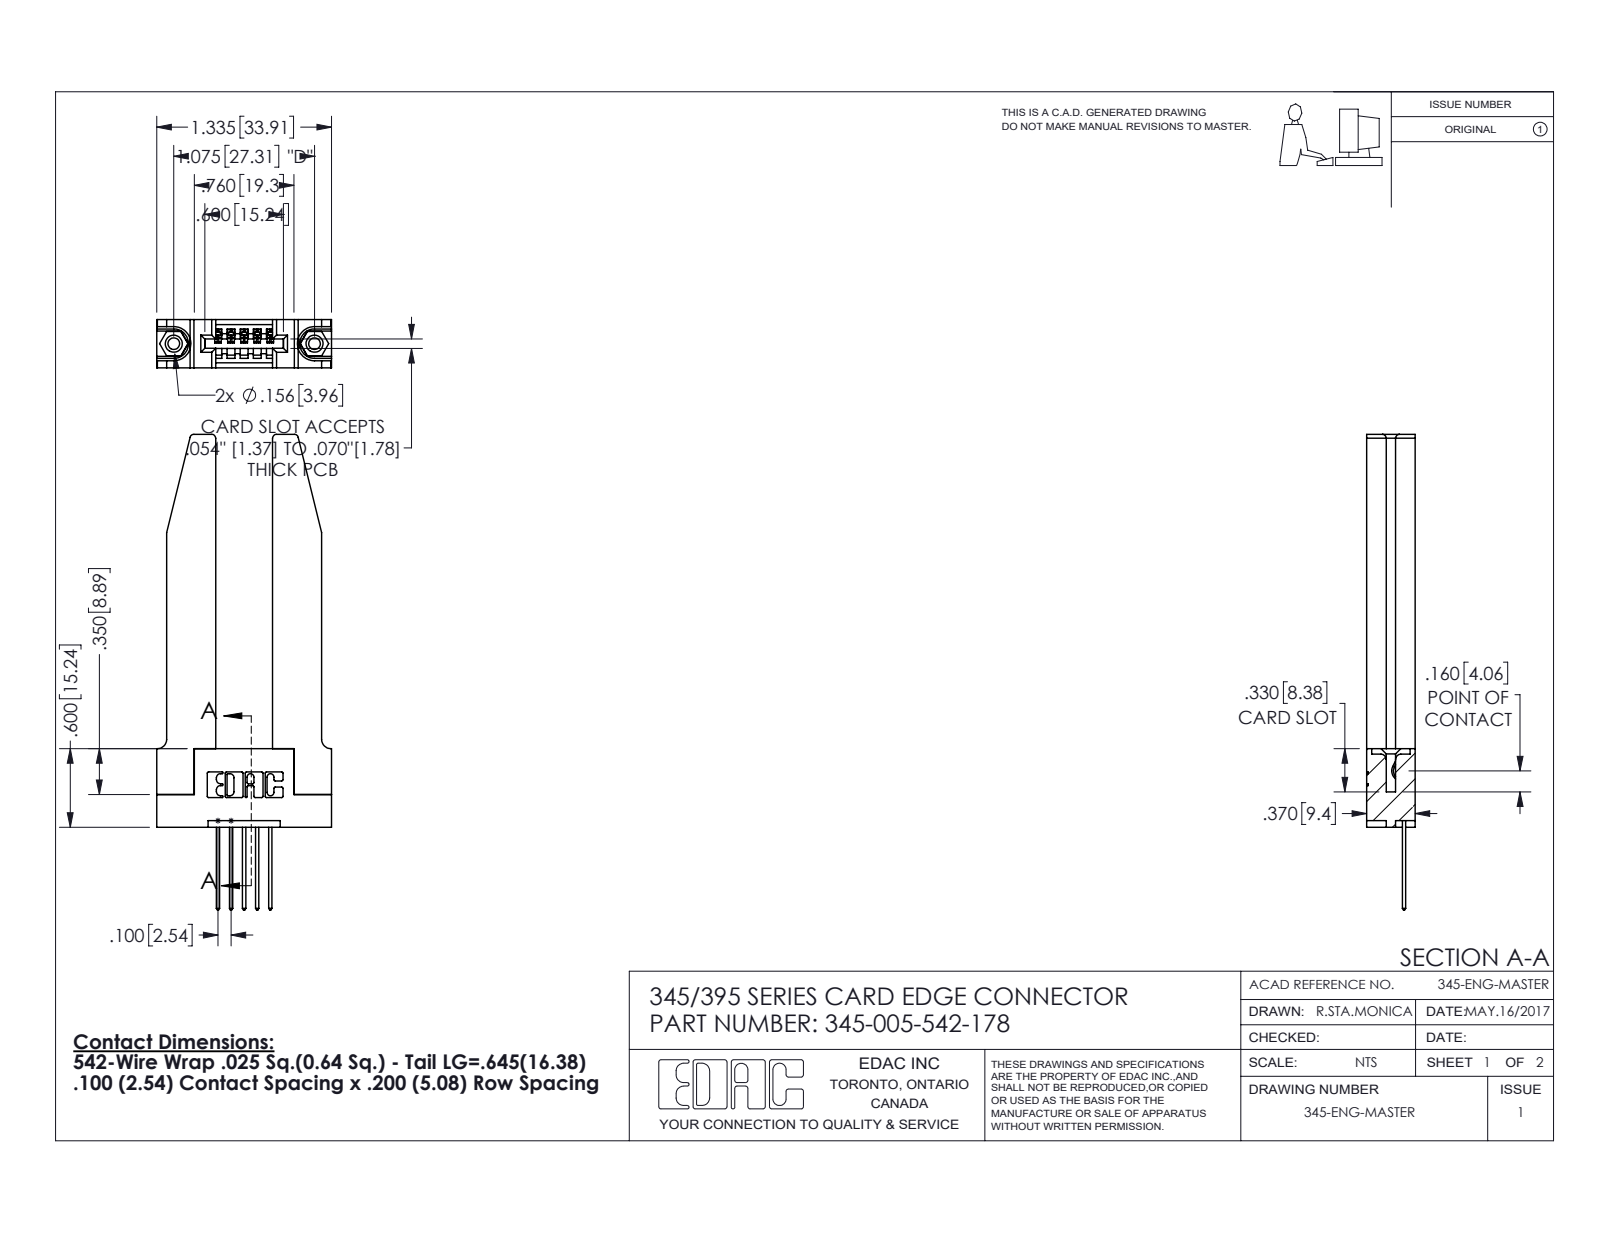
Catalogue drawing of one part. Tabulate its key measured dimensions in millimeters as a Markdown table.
| quantity | value |
| --- | --- |
| part name | 345 Part_Flush Mounting Lugs - 0.156 Dia-TH; 345-292-001_345-293-142; 345-220-078_345-220-078; 345-250-001_345-250-001-102 (+1 more) |
| STEP written by | SolidWorks 2016 (CONFIG_CONTROL_DESIGN) |
| units | millimeters |
| bodies | 10 solids, 650 faces (422 planar, 176 cylindrical, 52 other) |
| overall size | 92.3 × 33.9 × 9.4 |
| volume | 10 700 mm³ |
| surface area | 10 310 mm² |
| round holes (diameter × count) | 2.3 × 2, 3.2 × 2, 4 × 2, 1.6 × 1 |
| round bosses / shafts (diameter × count) | 3.9 × 2 |
| partial cylindrical surfaces (radius × count) | 0.3 × 22, 0.2 × 10, 0.3 × 10, 0.8 × 8, 0.2 × 6, 0.8 × 6, 0.7 × 3, 0.8 × 2 |
| main face-to-face distances | 9.4, 3.8, 5.6, 11, 1.8, 3.8, 5.1, 2, 7.6, 2.4 |
| hole center spacings | 6.9, 21.5, 27.3 |
